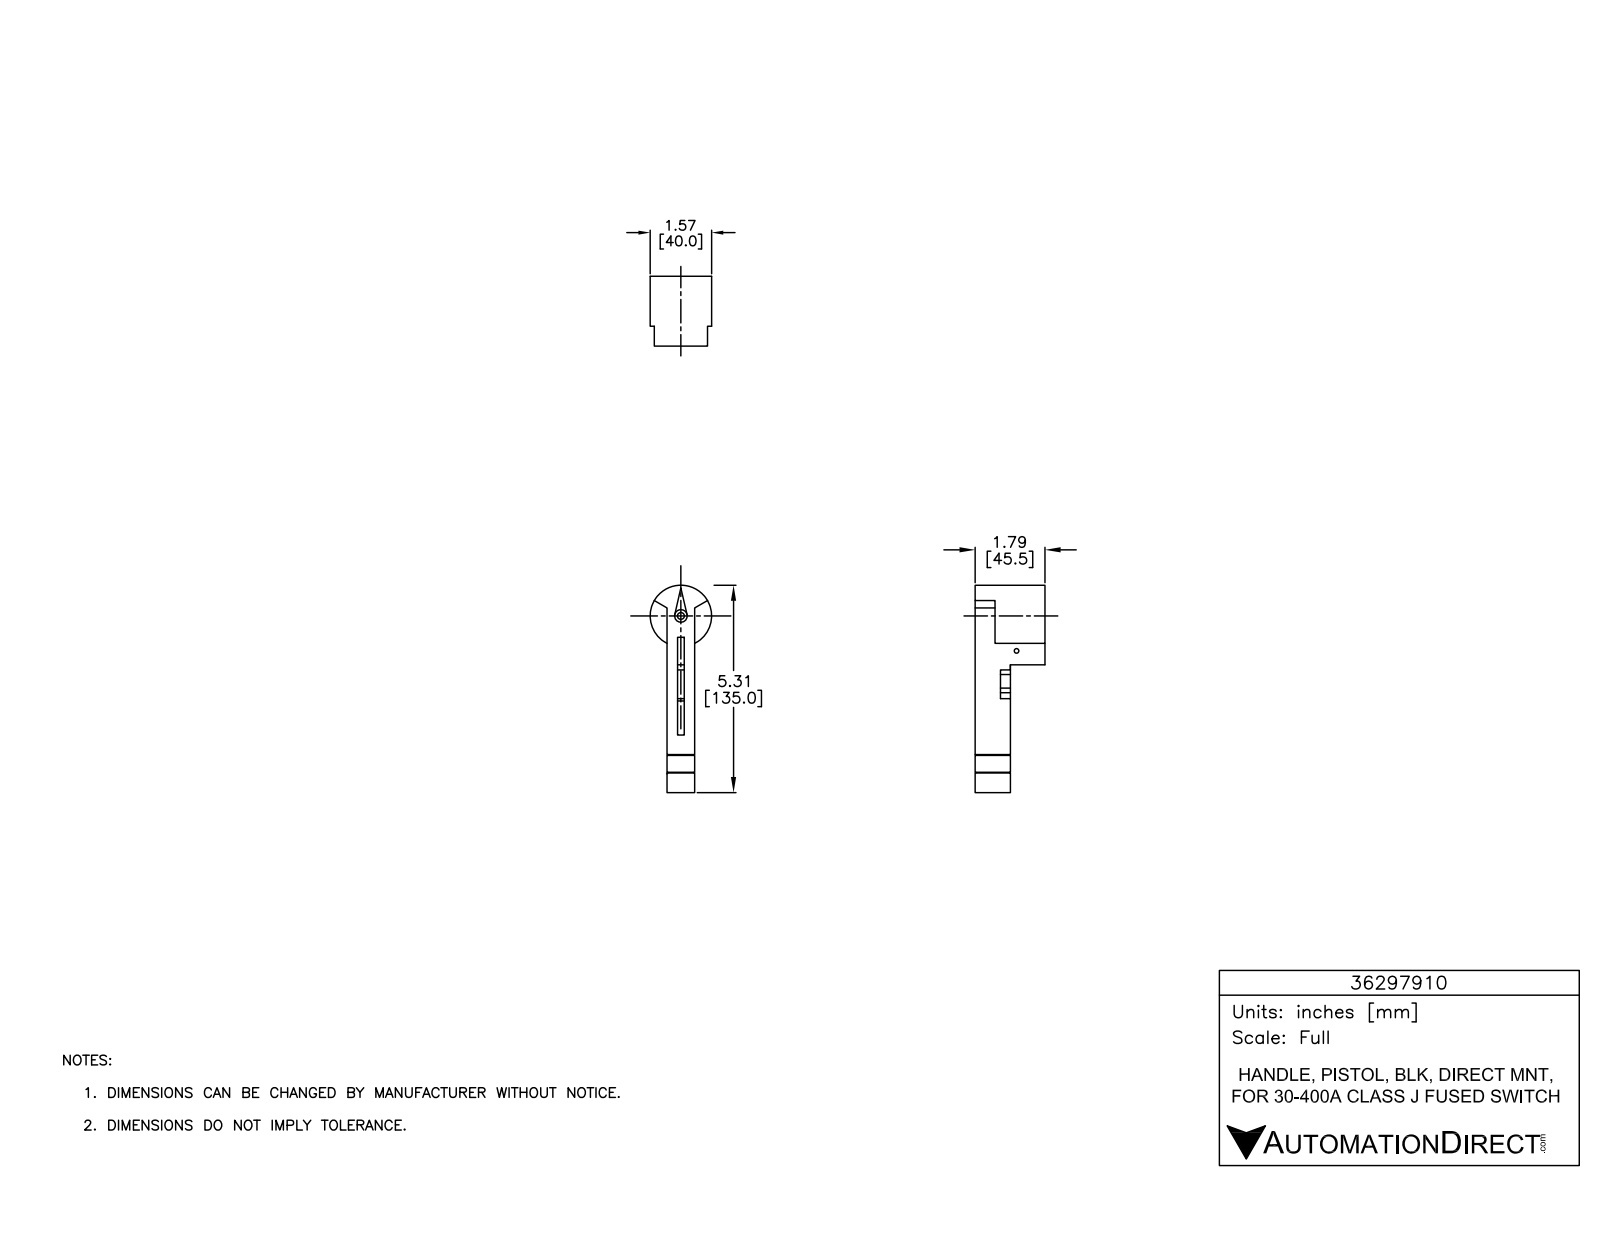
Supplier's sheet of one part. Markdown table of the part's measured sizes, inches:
| quantity | value |
| --- | --- |
| part name | 36297910 |
| STEP written by | SolidWorks 2015 (AUTOMOTIVE_DESIGN) |
| units | inches |
| bodies | 1 solid, 124 faces (109 planar, 15 cylindrical, 0 other) |
| overall size | 5.315 × 1.791 × 1.575 |
| volume | 4.734 in³ |
| surface area | 39.01 in² |
| round holes (diameter × count) | 0.118 × 1, 0.177 × 1, 0.236 × 1, 0.323 × 1 |
| round bosses / shafts (diameter × count) | 1.575 × 1 |
| main face-to-face distances | 0.709, 0.441, 0.268, 0.906, 0.173, 0.886, 1.791, 0.394, 0.055, 0.654 |
| hole center spacings | 0.591 |
